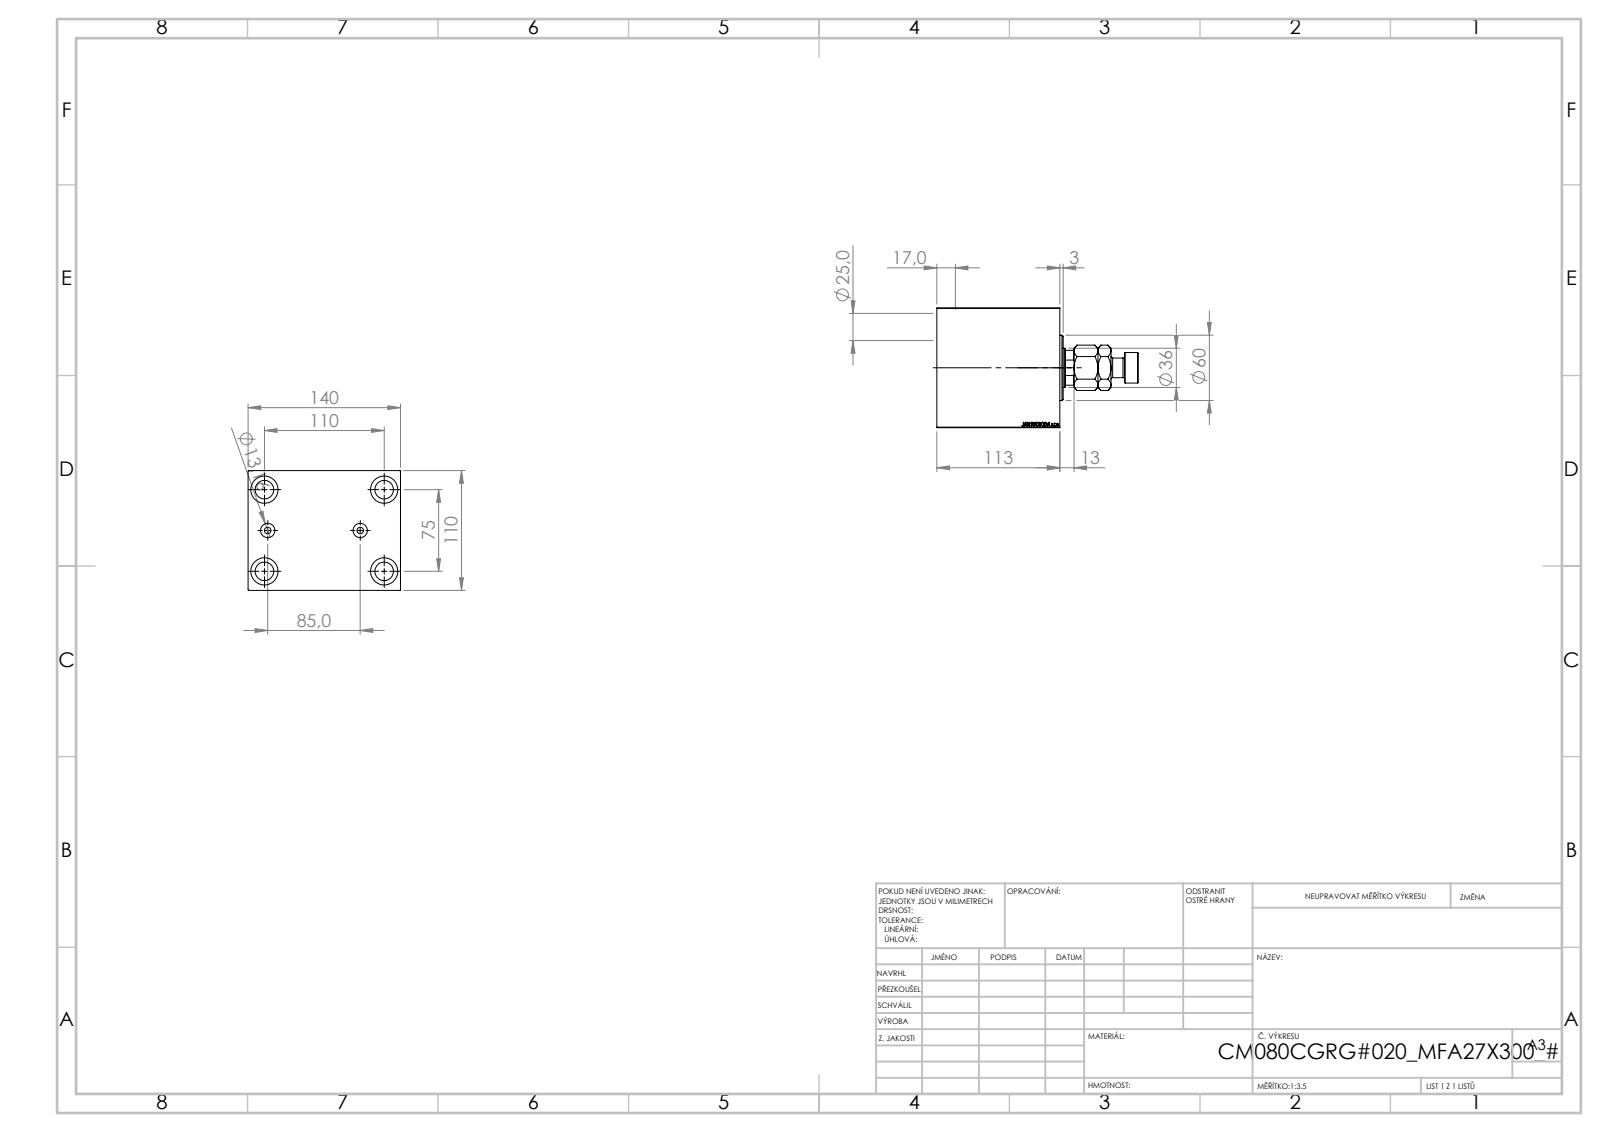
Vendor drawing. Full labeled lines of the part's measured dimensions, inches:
Part name (STEP PRODUCT): V450CM_C_Body; V450CM_VC_B; MFA; V450CM_C_VCP
STEP written by: SolidWorks 2019 (CONFIG_CONTROL_DESIGN)
Units: inches
Bodies: 4 solids, 915 faces (427 planar, 62 cylindrical, 426 other)
Overall size (bounding box): 7.323 × 5.512 × 4.331
Volume: 95.38 in³ · Surface area: 276 in²
Round holes (diameter × count): ⌀0.669 ×4, ⌀0.984 ×4, ⌀0.236 ×2, ⌀0.518 ×2, ⌀1.004 ×1, ⌀1.417 ×1, ⌀1.555 ×1, ⌀3.15 ×1, ⌀3.228 ×1, ⌀3.425 ×1
Round bosses / shafts (diameter × count): ⌀2.362 ×1, ⌀1.102 ×1, ⌀0.709 ×1
Partial cylindrical surfaces — rounded edges, fillets, slot ends (radius × count): R0.689 ×1
Main face-to-face distances: 4.331, 5.512, 4.449, 2.254, 2.195, 4.055, 0.787, 0.394, 3.268, 1.801
Hole centre spacings: 1.556, 2.621, 4.113, 1.673, 2.953, 4.331, 5.242, 3.346
